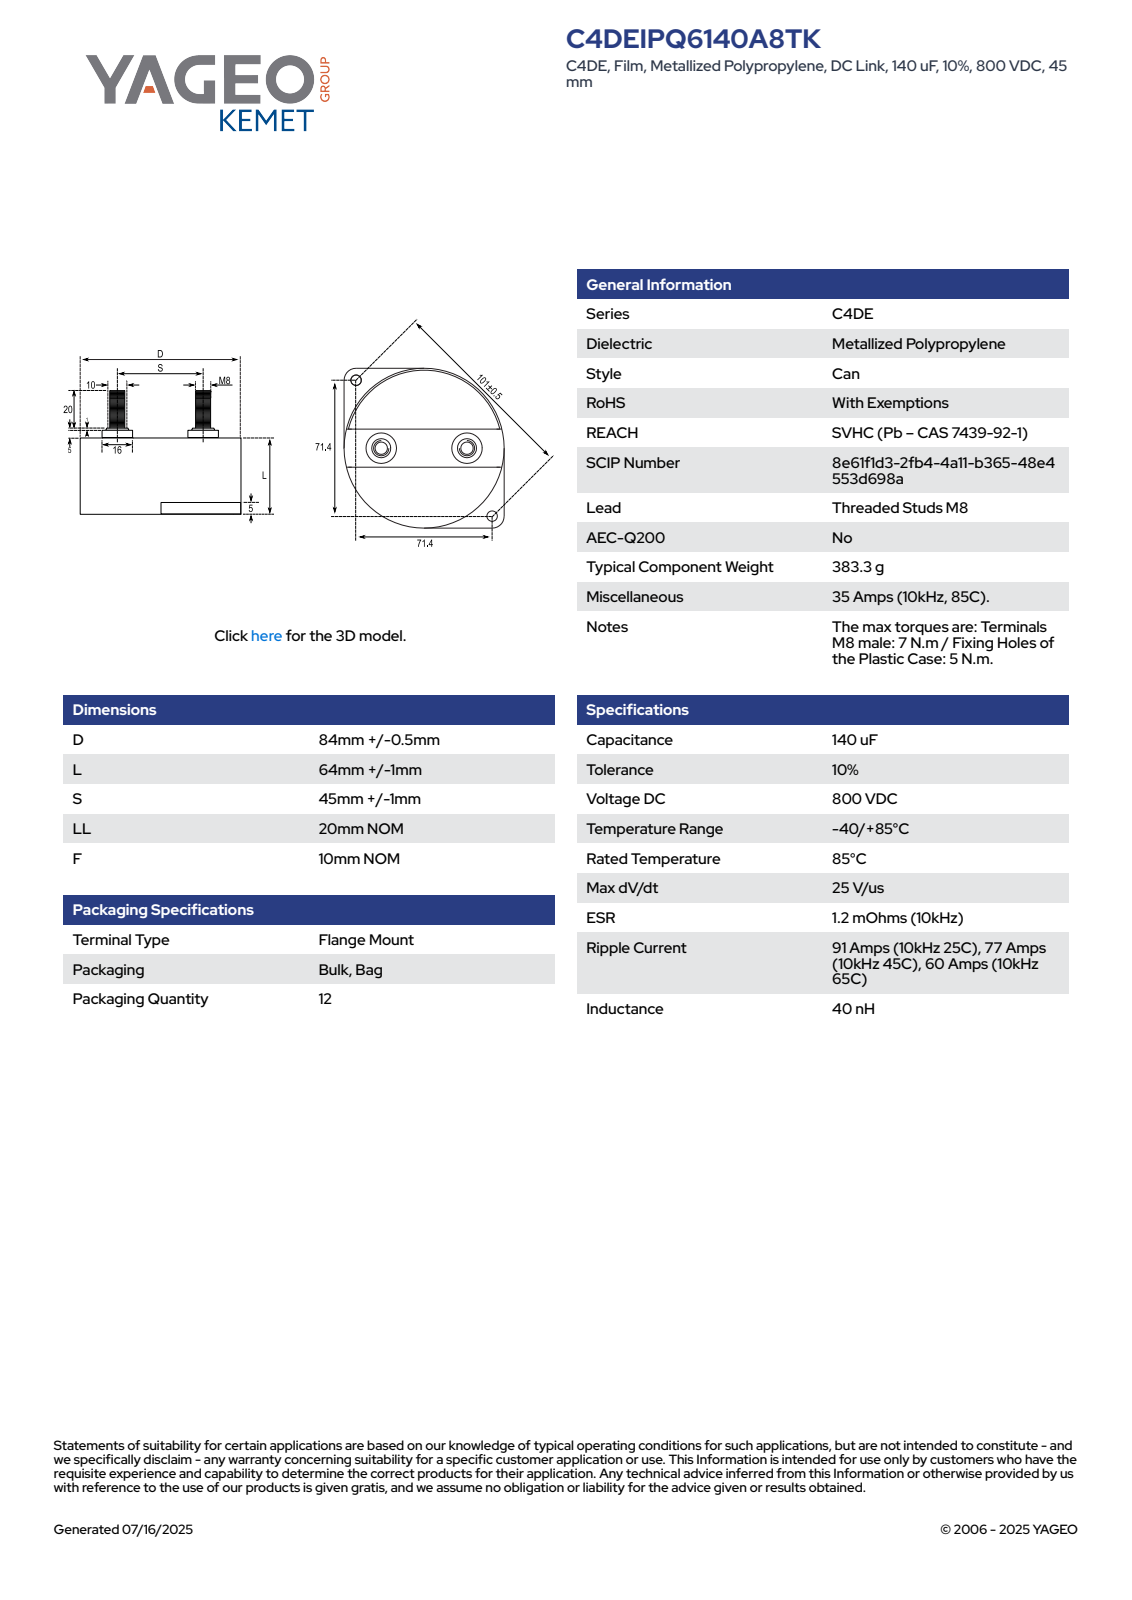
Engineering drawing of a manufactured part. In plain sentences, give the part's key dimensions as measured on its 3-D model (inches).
The part is named "CFP_C44DE_84X64_D84.5L65S46LL20". Its 3-D file was written by "SolidWorks 2021 (AUTOMOTIVE_DESIGN)". It is 1 solid with 103 faces: 37 planar, 31 cylindrical and 35 other. Overall it measures 3.583 by 3.327 by 3.327 inches. Its volume is 22.71 cubic inches and its surface area 49.12 square inches. Round holes: 2 of diameter 0.217. Round bosses or shafts: 2 of diameter 0.63, 2 of diameter 0.394, 2 of diameter 0.315, 1 of diameter 3.327, 1 of diameter 3.15. Partial cylindrical surfaces (rounded edges, fillets, slot ends): 2 of radius 0.394, 1 of radius 1.664. The main face-to-face distances are 2.559, 0.197, 2.559, 2.363, 2.362, 3.327, 2.756, 0.196, 3.583, 3.386. The hole center spacings are 3.996.
